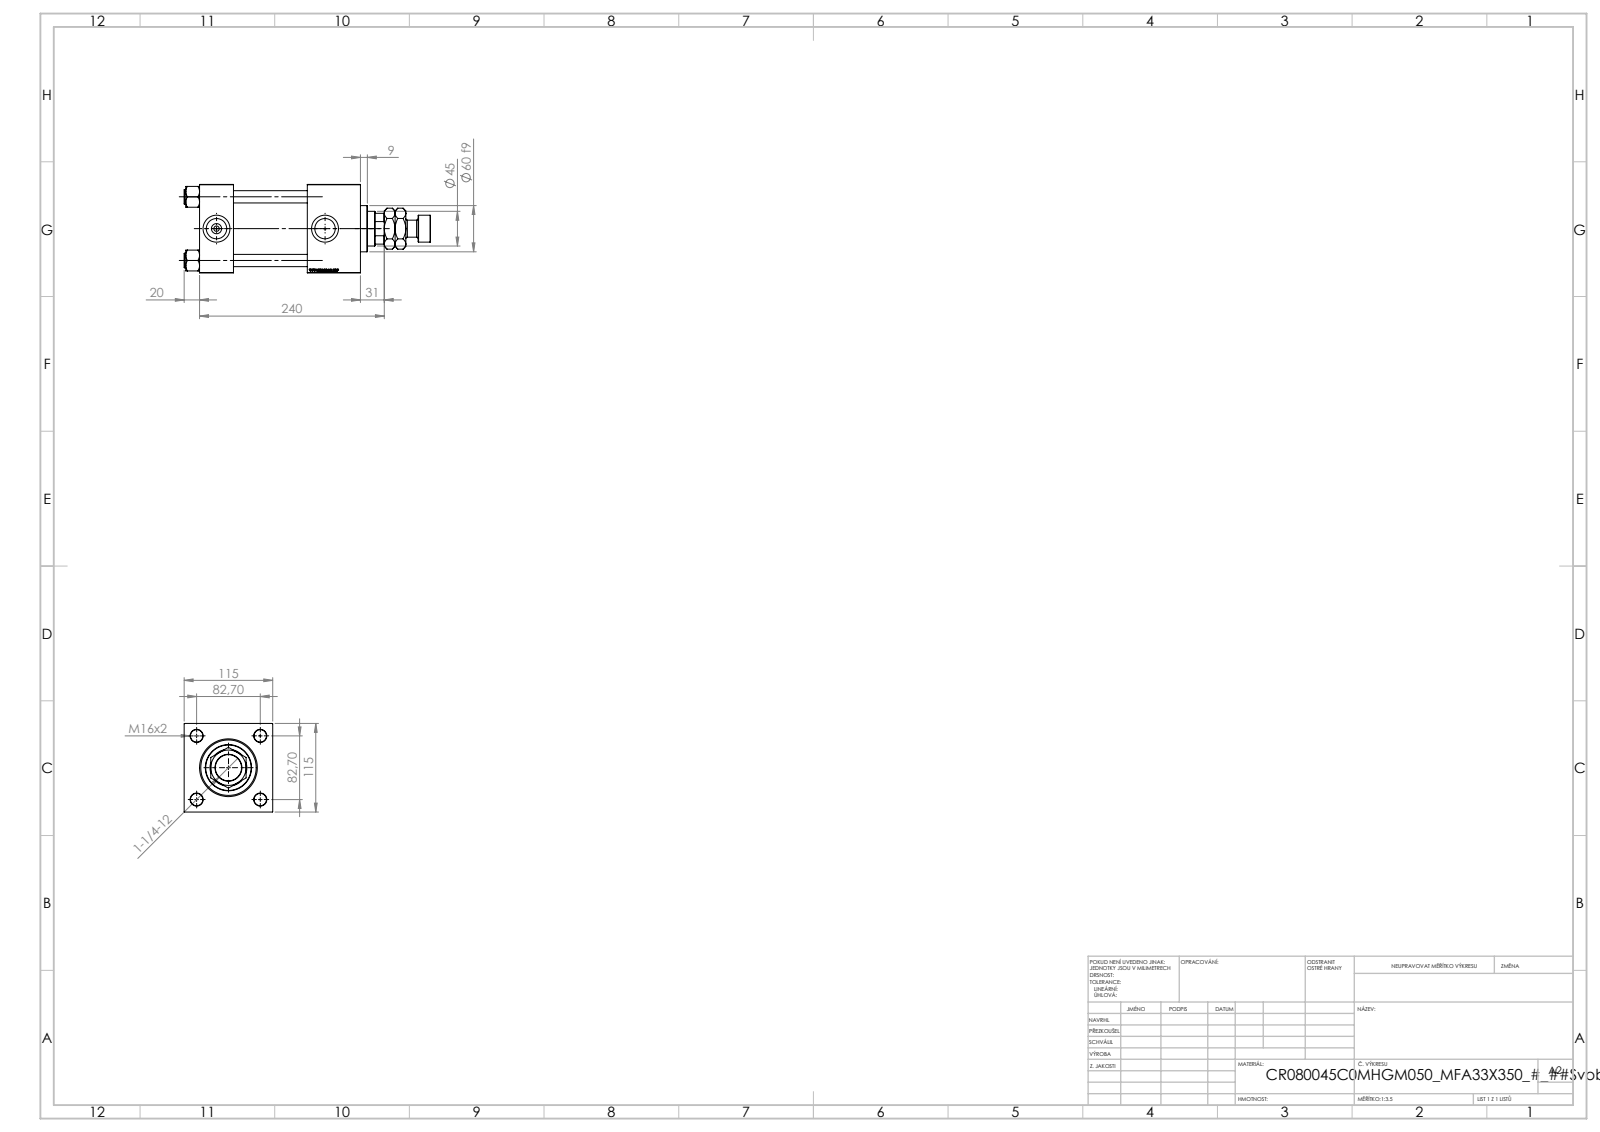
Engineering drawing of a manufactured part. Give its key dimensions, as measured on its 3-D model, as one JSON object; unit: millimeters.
{"part_name": "NUT_M5_C; V215CR_C_Body; V215_VC_A; V215CR_C_TYCINKA (+2 more)", "step_written_by": "SolidWorks 2019 (CONFIG_CONTROL_DESIGN)", "units": "millimeters", "bodies": {"solids": 12, "faces": 1248, "planar": 590, "cylindrical": 90, "other": 568}, "overall_size": [320, 115, 115], "volume_mm3": 1987000, "surface_area_mm2": 311616, "round_holes": [[16, 4], [7, 2], [26.44, 2], [35, 2], [31.5, 1], [45, 1], [48, 1], [61, 1], [72, 1], [80, 1]], "round_bosses_or_shafts": [[19, 4], [86, 1], [60, 1], [35, 1], [22, 1]], "partial_cylinders_radius": [[22, 1]], "face_to_face_distances": [115, 44, 209, 165, 140, 96, 69, 46, 50, 180.3], "hole_center_spacings": [58.48, 82.7, 116.96, 141]}
